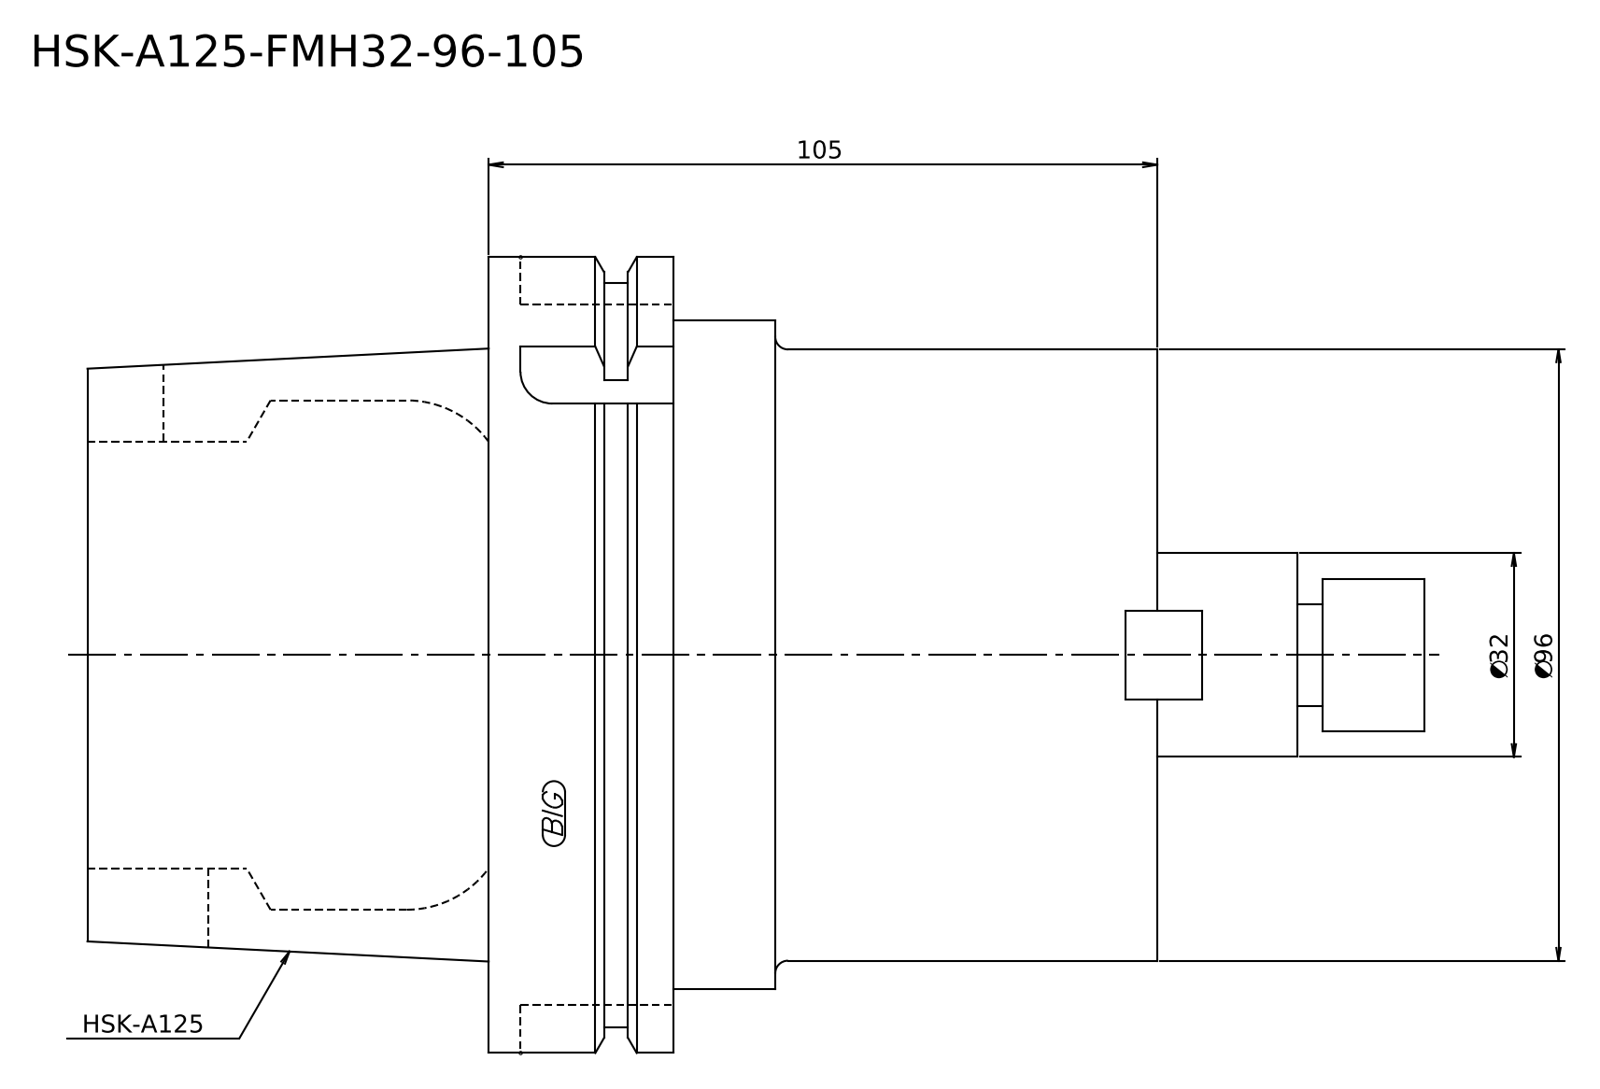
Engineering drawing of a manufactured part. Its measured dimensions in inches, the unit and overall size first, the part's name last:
Units: inches
Overall size (bounding box): 7.48 × 4.921 × 4.921
Round bosses / shafts (diameter × count): ⌀4.921 ×1, ⌀4.606 ×1, ⌀4.134 ×1, ⌀3.78 ×1, ⌀1.26 ×1
Main face-to-face distances: 6.614, 4.134, 2.48, 2.992, 1.142, 3.622, 2.362, 0.63, 1.772, 4.252
Volume: 83.54 in³ · Surface area: 125.3 in²
Bodies: 1 solid, 18 faces (8 planar, 6 cylindrical, 4 other)
STEP written by: Kubotek KeyCreator 2011 V10.0.2 (22737) (automotive_design)
